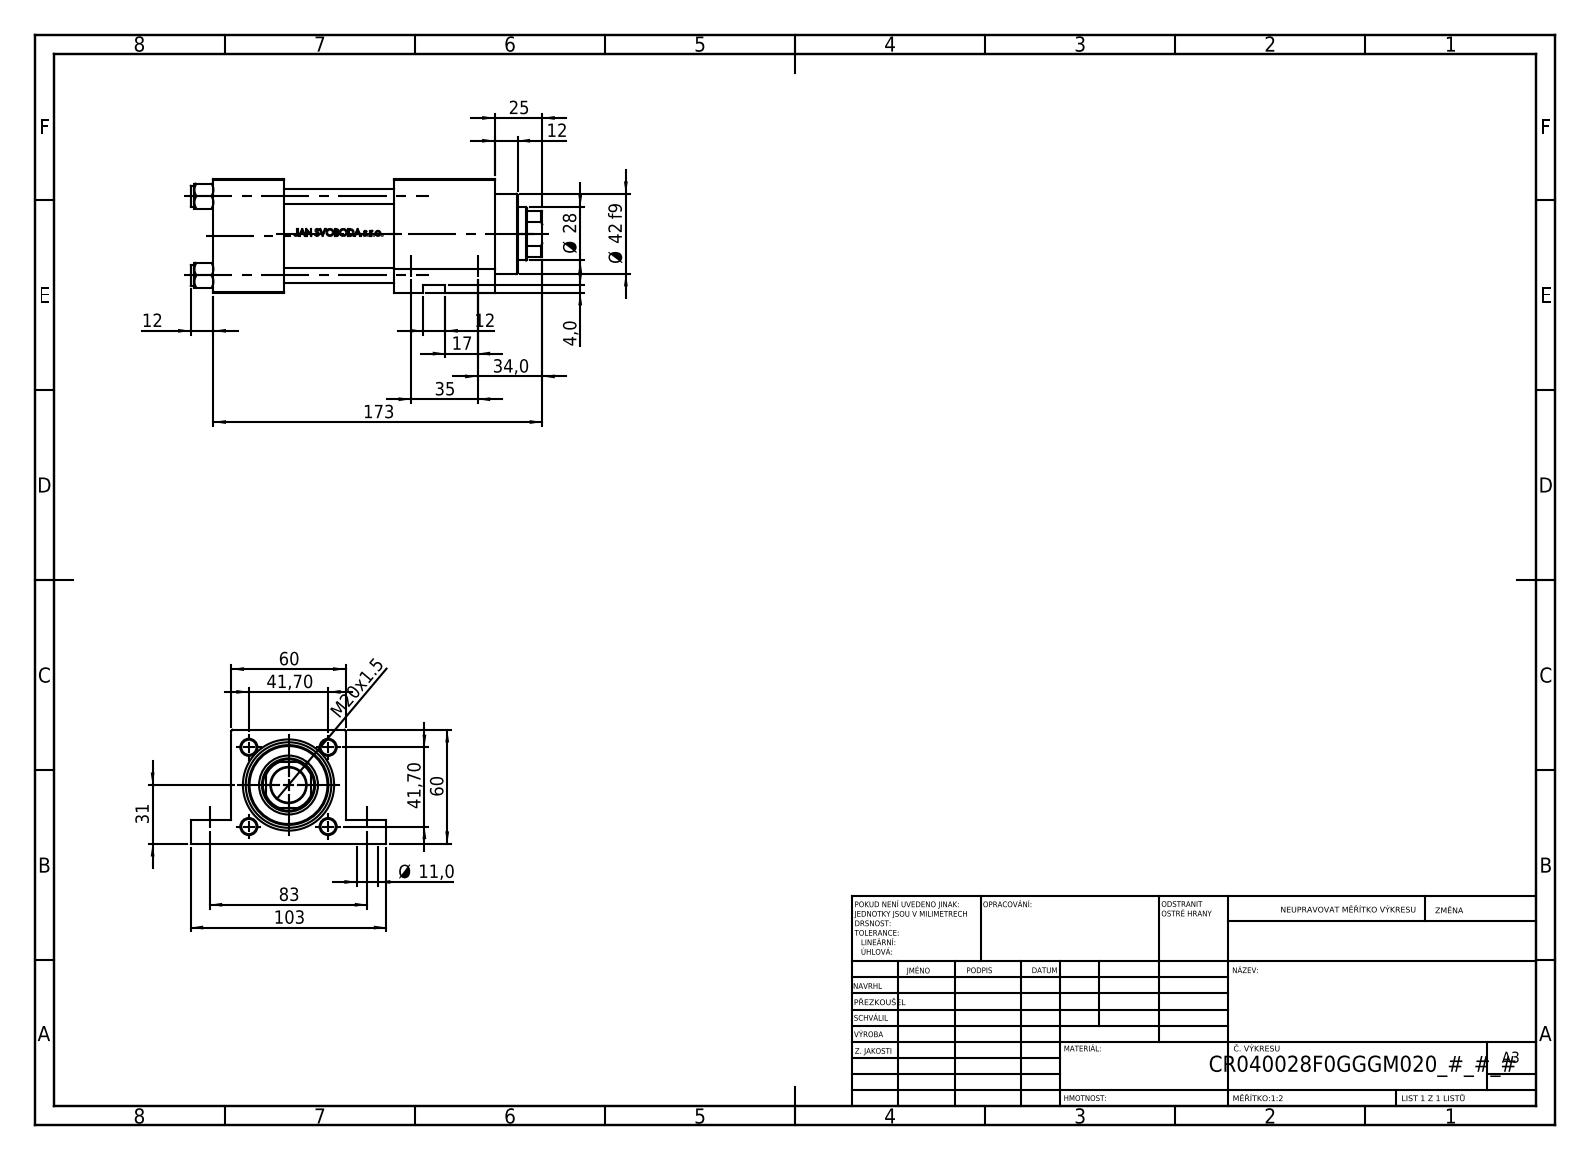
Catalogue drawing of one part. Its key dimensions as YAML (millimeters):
part_name: "V215CR_VCP_F; NUT_M5_F; V215CR_F_TYCINKA; V215CR_F_Body (+1 more)"
step_written_by: "SolidWorks 2019 (CONFIG_CONTROL_DESIGN)"
units: millimeters
bodies: {solids: 11, faces: 1121, planar: 438, cylindrical: 143, other: 540}
overall_size: [185, 103, 60]
volume: 444851
surface_area: 117845
round_holes:
  - {diameter: 8, count: 4}
  - {diameter: 7, count: 2}
  - {diameter: 11, count: 2}
  - {diameter: 11, count: 2}
  - {diameter: 16.66, count: 2}
  - {diameter: 24, count: 2}
  - {diameter: 18.5, count: 1}
  - {diameter: 28, count: 1}
  - {diameter: 31, count: 1}
  - {diameter: 40, count: 1}
  - {diameter: 45, count: 1}
round_bosses_or_shafts:
  - {diameter: 11, count: 4}
  - {diameter: 46, count: 1}
  - {diameter: 42, count: 1}
partial_cylinders:
  - {radius: 13.5, count: 1}
face_to_face_distances: [60, 37, 95, 58, 148, 111, 53, 12.5, 47.5, 38]
hole_center_spacings: [41.7, 28.79, 30.2, 35, 42.09, 50.06, 58.97, 83]
